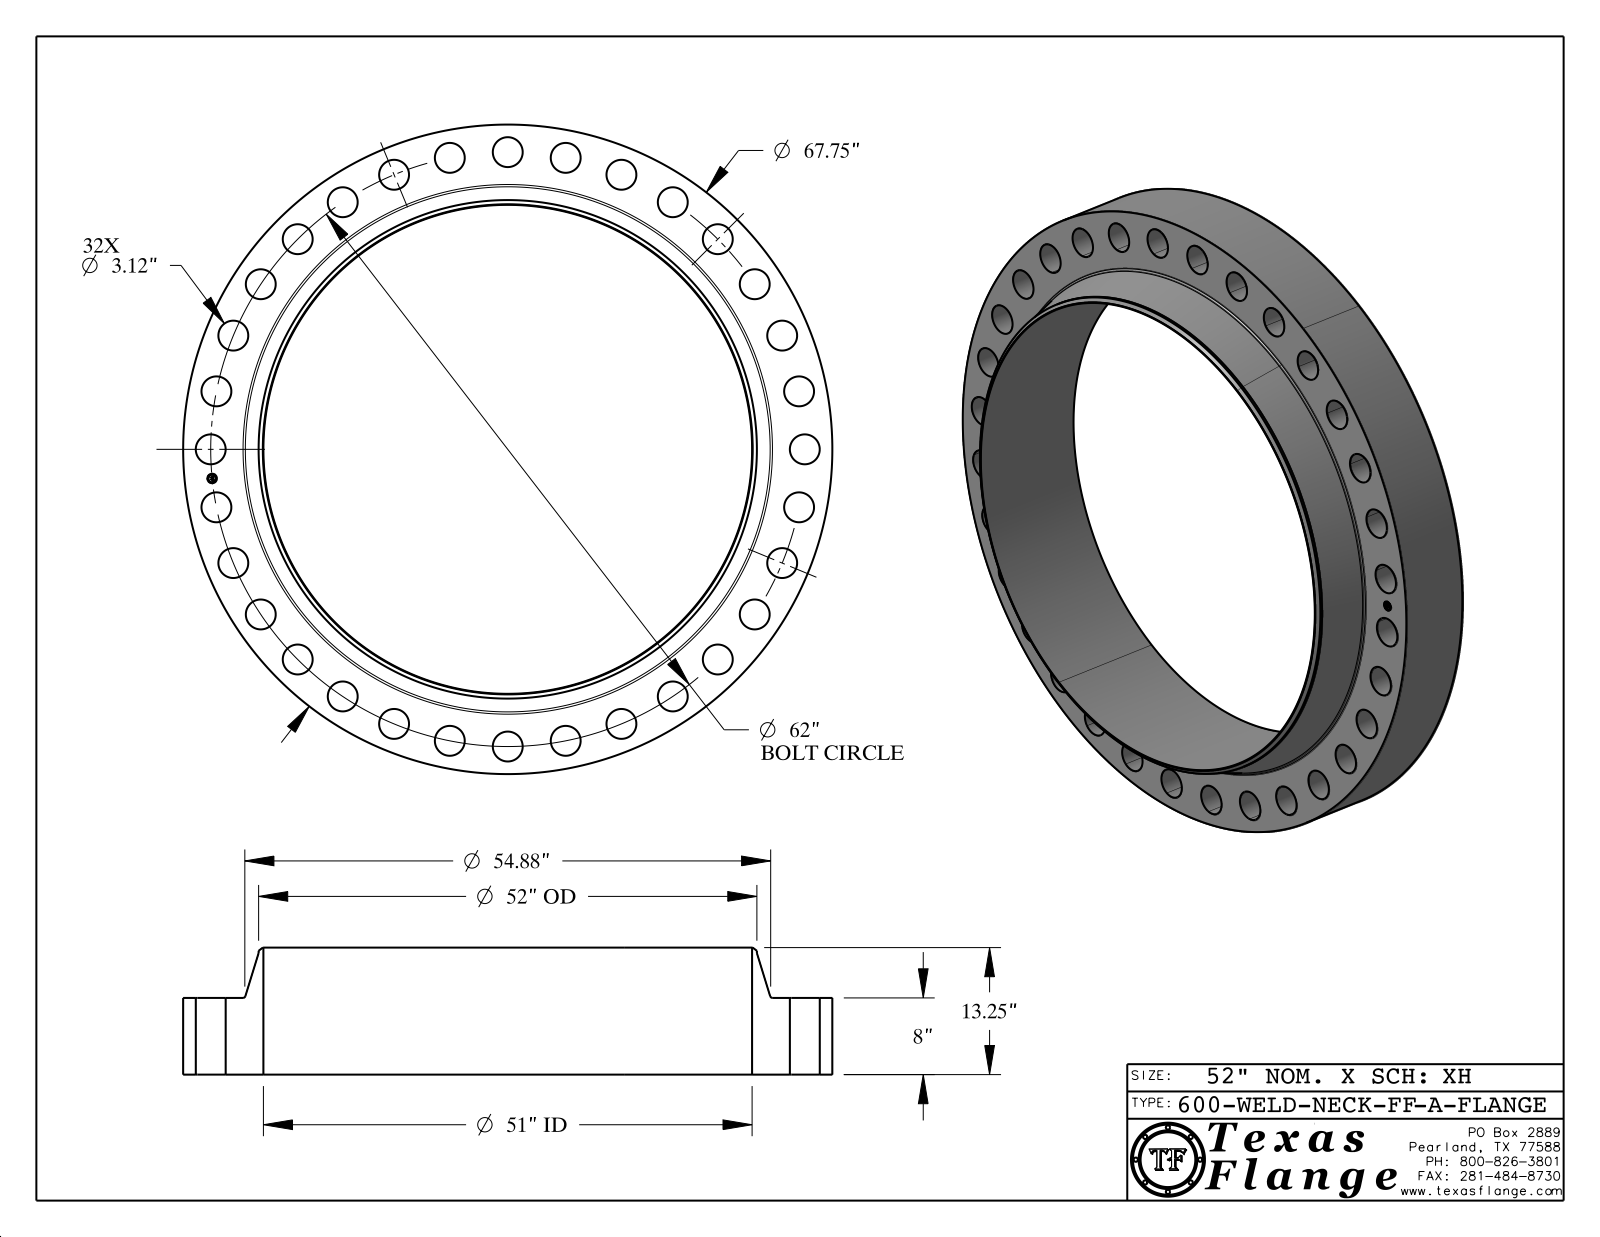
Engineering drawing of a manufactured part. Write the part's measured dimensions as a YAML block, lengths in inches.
part_name: "600-WELD-NECK-FF, Series A"
step_written_by: "CATIA V5 STEP AP214 (AUTOMOTIVE_DESIGN)"
units: inches
bodies: {solids: 1, faces: 464, planar: 368, cylindrical: 90, other: 6}
overall_size: [67.75, 67.75, 13.25]
volume: 11515
surface_area: 9598
round_holes:
  - {diameter: 3.12, count: 32}
  - {diameter: 1, count: 1}
  - {diameter: 51, count: 1}
round_bosses_or_shafts:
  - {diameter: 0.061, count: 8}
  - {diameter: 67.75, count: 1}
  - {diameter: 52, count: 1}
  - {diameter: 0.788, count: 1}
face_to_face_distances: [8, 13.25, 5.25, 0.015, 7.985, 5.265, 0.298, 0.292, 0.054, 0.193]
hole_center_spacings: [59.33, 31, 6.077, 23.726, 60.809, 29.226, 34.445, 39.332]
